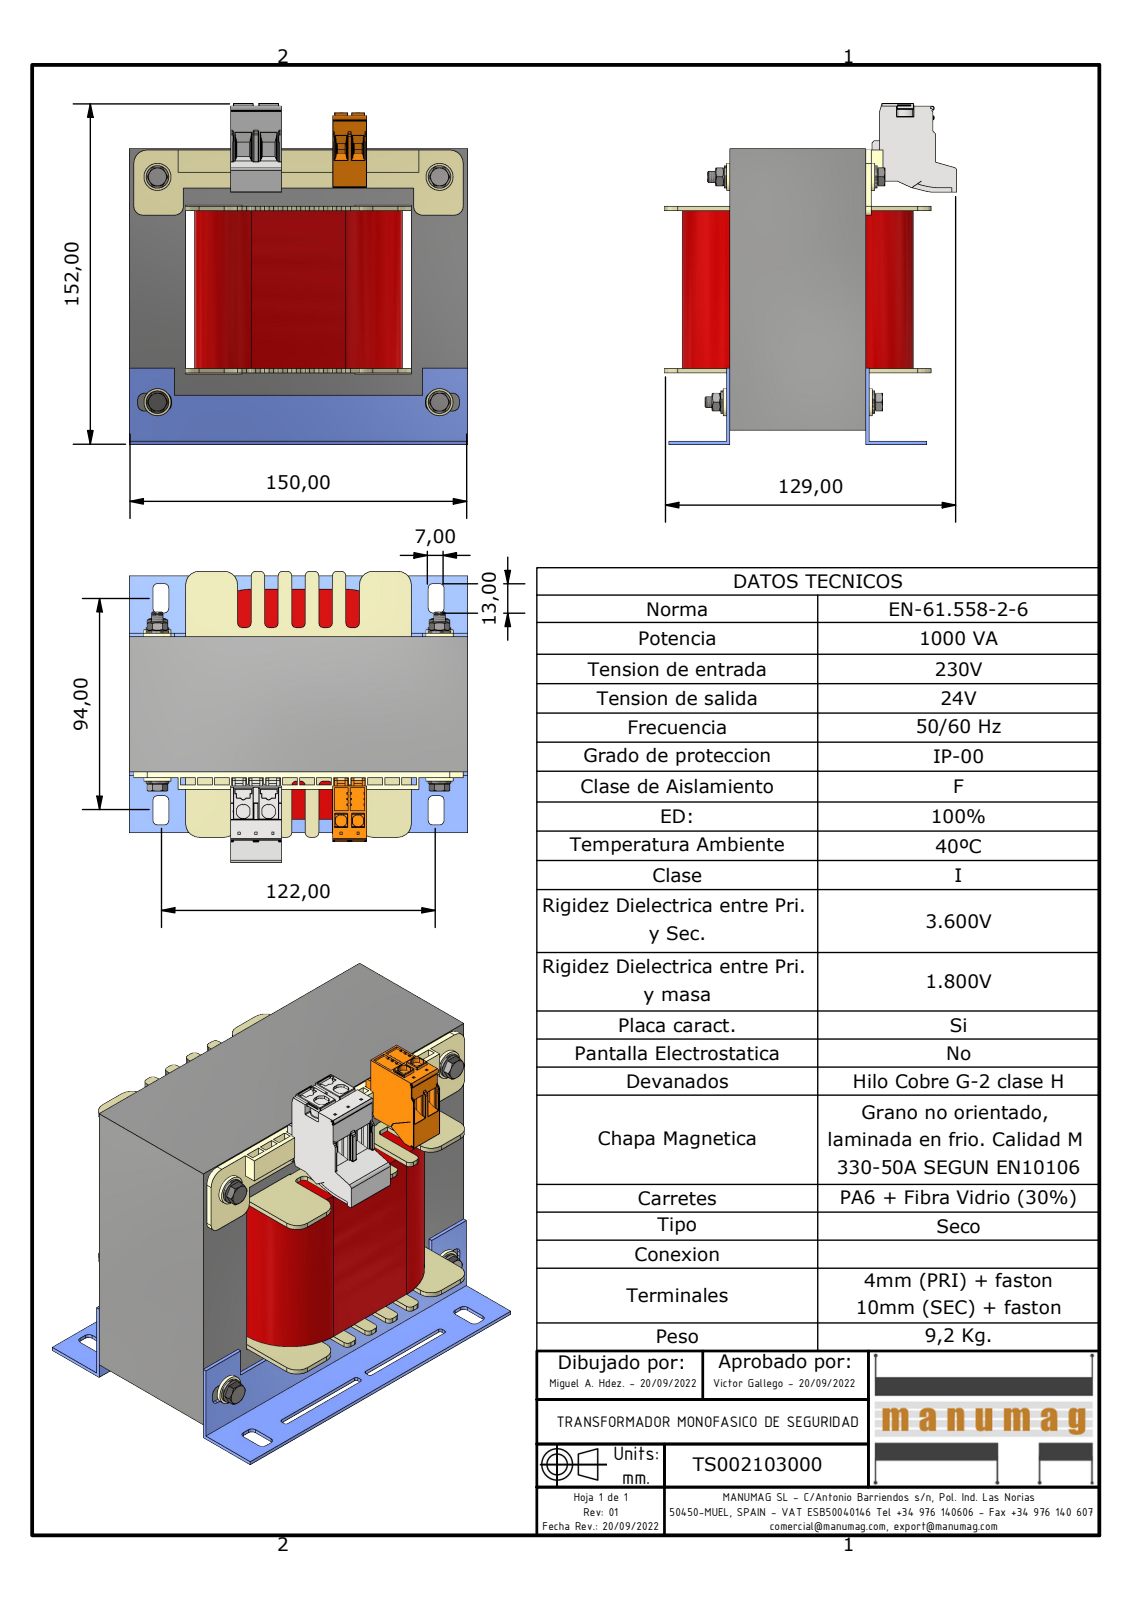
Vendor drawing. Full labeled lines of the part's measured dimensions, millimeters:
Part name (STEP PRODUCT): TS002103000; EI150 x 125 - 60 (RC50); AF50DIN; EI150 (+7 more)
STEP written by: Autodesk Inventor 2023 (AUTOMOTIVE_DESIGN)
Units: millimetres
Bodies: 31 solids, 4190 faces (3354 planar, 596 cylindrical, 240 other)
Overall size (bounding box): 151.6 × 150 × 129.25
Volume: 1 390 000 mm³ · Surface area: 226 391 mm²
Round holes (diameter × count): ⌀4.13 ×4, ⌀5 ×4, ⌀5.3 ×4, ⌀8 ×4
Round bosses / shafts (diameter × count): ⌀12 ×4, ⌀10 ×4, ⌀6.7 ×4, ⌀5.9 ×4, ⌀4.57 ×4
Partial cylindrical surfaces — rounded edges, fillets, slot ends (radius × count): R0.15 ×98, R0.2 ×85, R2 ×53, R0.3 ×37, R1 ×22, R0.1 ×14, R0.5 ×14, R6 ×10
Main face-to-face distances: 25, 100, 50, 60, 125, 1.5, 99.5, 25.5, 21, 75
Hole centre spacings: 100, 125, 160.08
